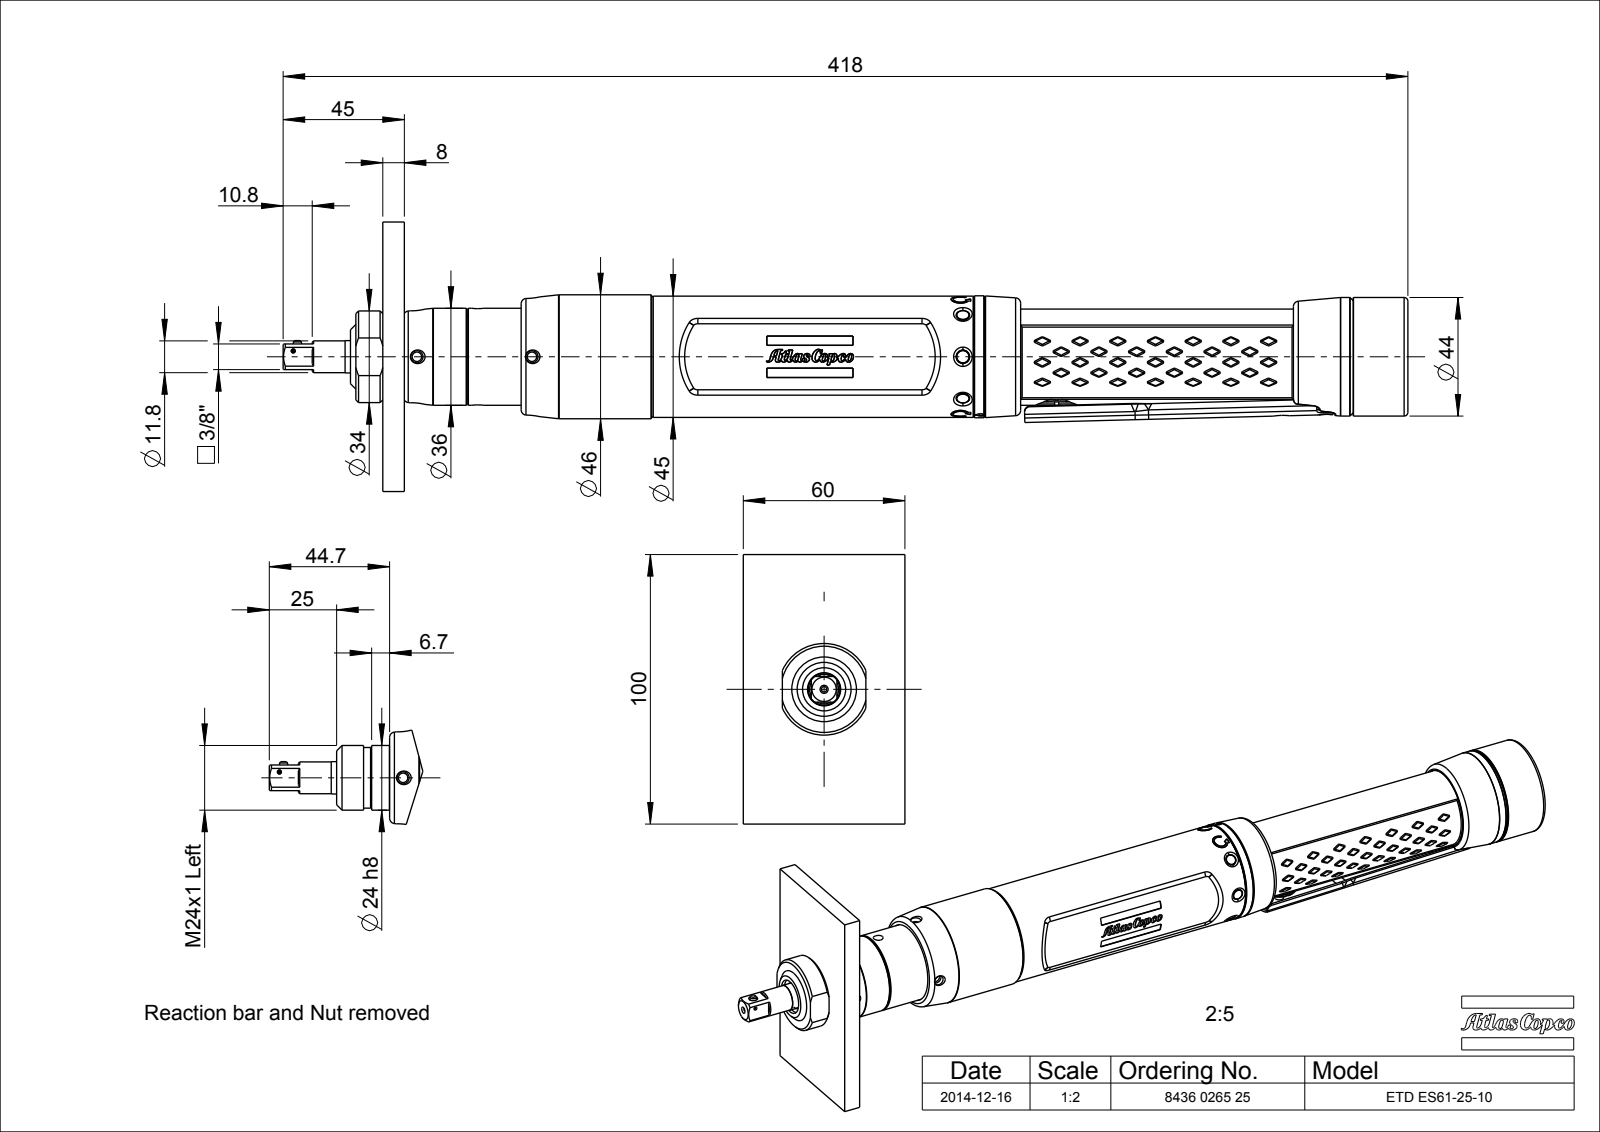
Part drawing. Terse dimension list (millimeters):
name: 4220388170_AF0; 4220388112_AF0; 4220388172_AF0_ASM; 4220388180_ASM (+8 more)
written by: PRO/ENGINEER BY PARAMETRIC TECHNOLOGY CORPORATION, 2013410 (CONFIG_CONTROL_DESIGN)
unit: mm
bodies: 43 solids, 5220 faces (2038 planar, 913 cylindrical, 2269 other)
size: 417.57 × 100 × 60
volume: 288 947 mm³; area: 238 703 mm²
holes: 12× ⌀2.64, 12× ⌀3.27, 12× ⌀3.6, 6× ⌀4.2, 5× ⌀2.5, 5× ⌀4.5, 5× ⌀5, 2× ⌀16, 1× ⌀1.5, 1× ⌀2, 1× ⌀2.2, 1× ⌀2.6
bosses: 9× ⌀2.2, 9× ⌀1.9, 9× ⌀1.57, 7× ⌀3.2, 3× ⌀2.92, 2× ⌀3.05, 2× ⌀2.54, 2× ⌀2.3
rounds: 60× R0.2, 33× R0.4, 28× R2, 18× R1, 14× R0.5, 12× R0.1, 10× R0.25, 6× R0.24
face distances: 8, 1.5, 60, 1, 349.17, 357.17, 347.67, 355.67, 20.2, 100
hole spacings: 6.2, 9.51, 14.67, 19.64, 23.72, 5.88, 13.44, 14.5
